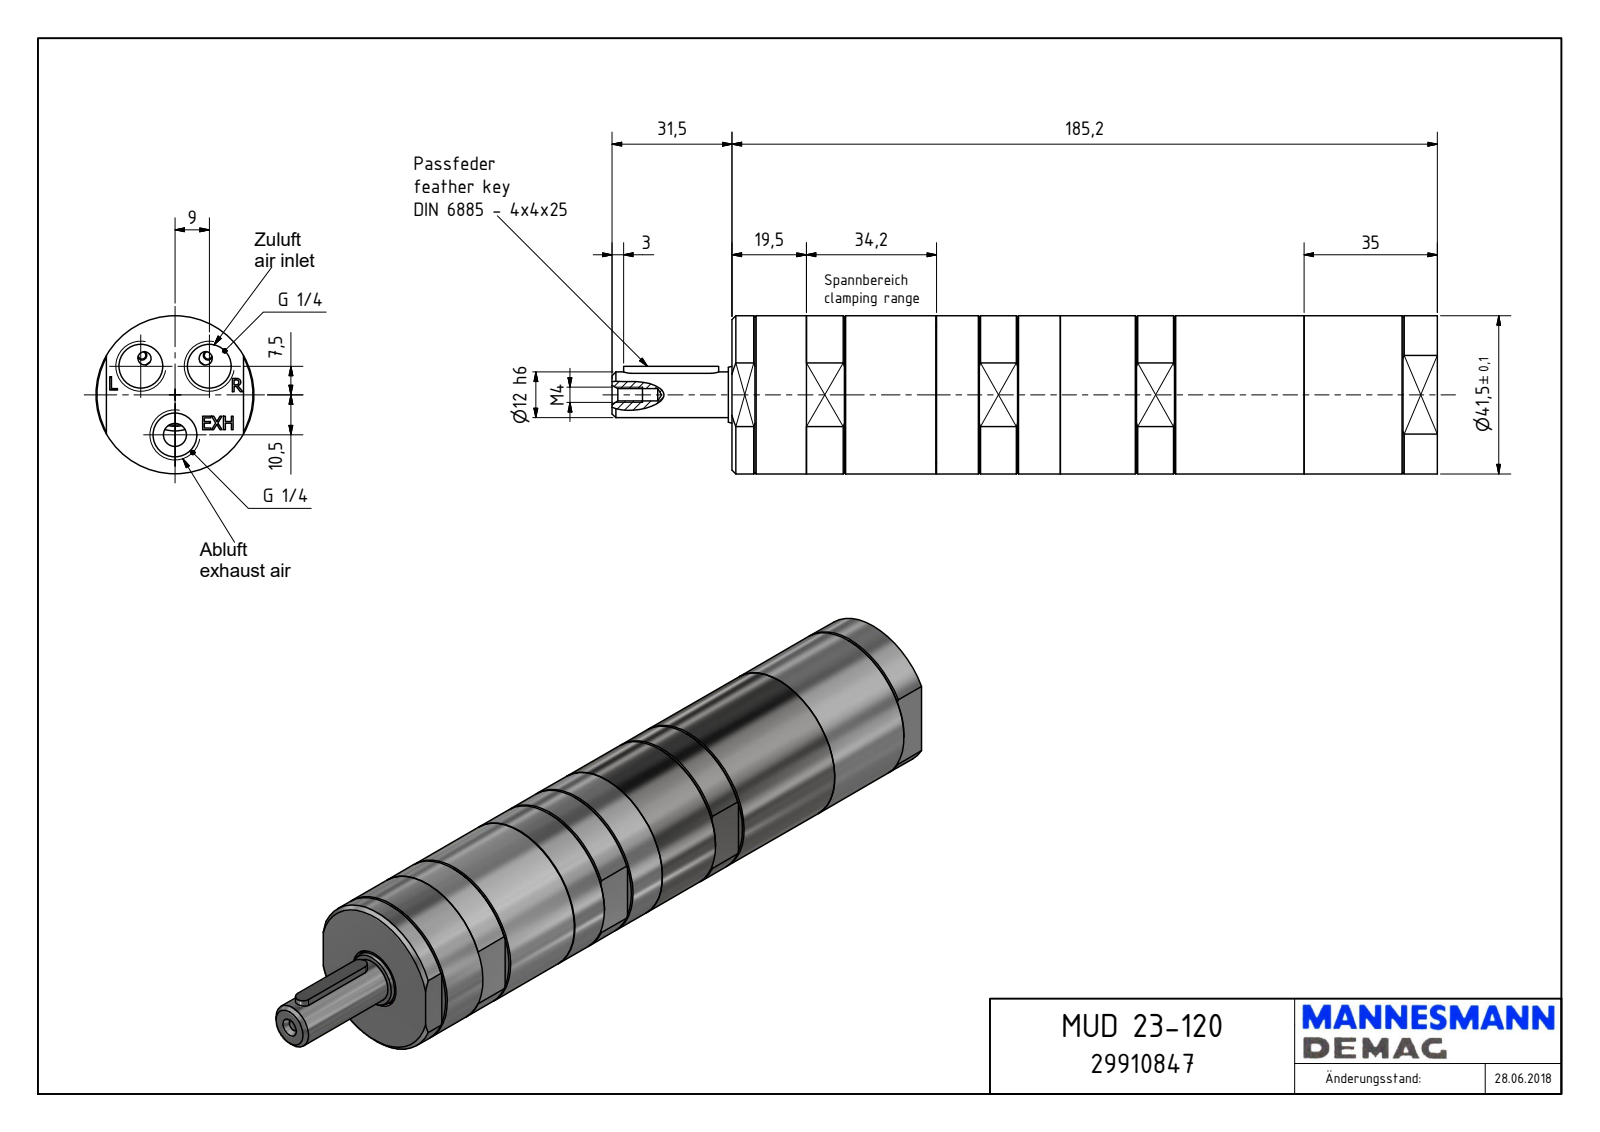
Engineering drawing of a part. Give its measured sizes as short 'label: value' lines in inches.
name: MUD 23-120_29910847
written by: Autodesk Inventor 2018 (AUTOMOTIVE_DESIGN)
unit: in
bodies: 1 solid, 162 faces (98 planar, 27 cylindrical, 37 other)
size: 8.531 × 1.634 × 1.634
volume: 15.18 in³; area: 46.9 in²
holes: 3× ⌀0.451, 1× ⌀0.128, 1× ⌀0.63
bosses: 1× ⌀1.634, 1× ⌀1.417, 1× ⌀0.589, 1× ⌀0.472
rounds: 2× R0.079
face distances: 7.291, 1.496, 0.039, 1.457, 2.106, 5.185, 2.114, 5.177, 6.894, 4.787
hole spacings: 0.461, 0.792, 0.413, 0.709
